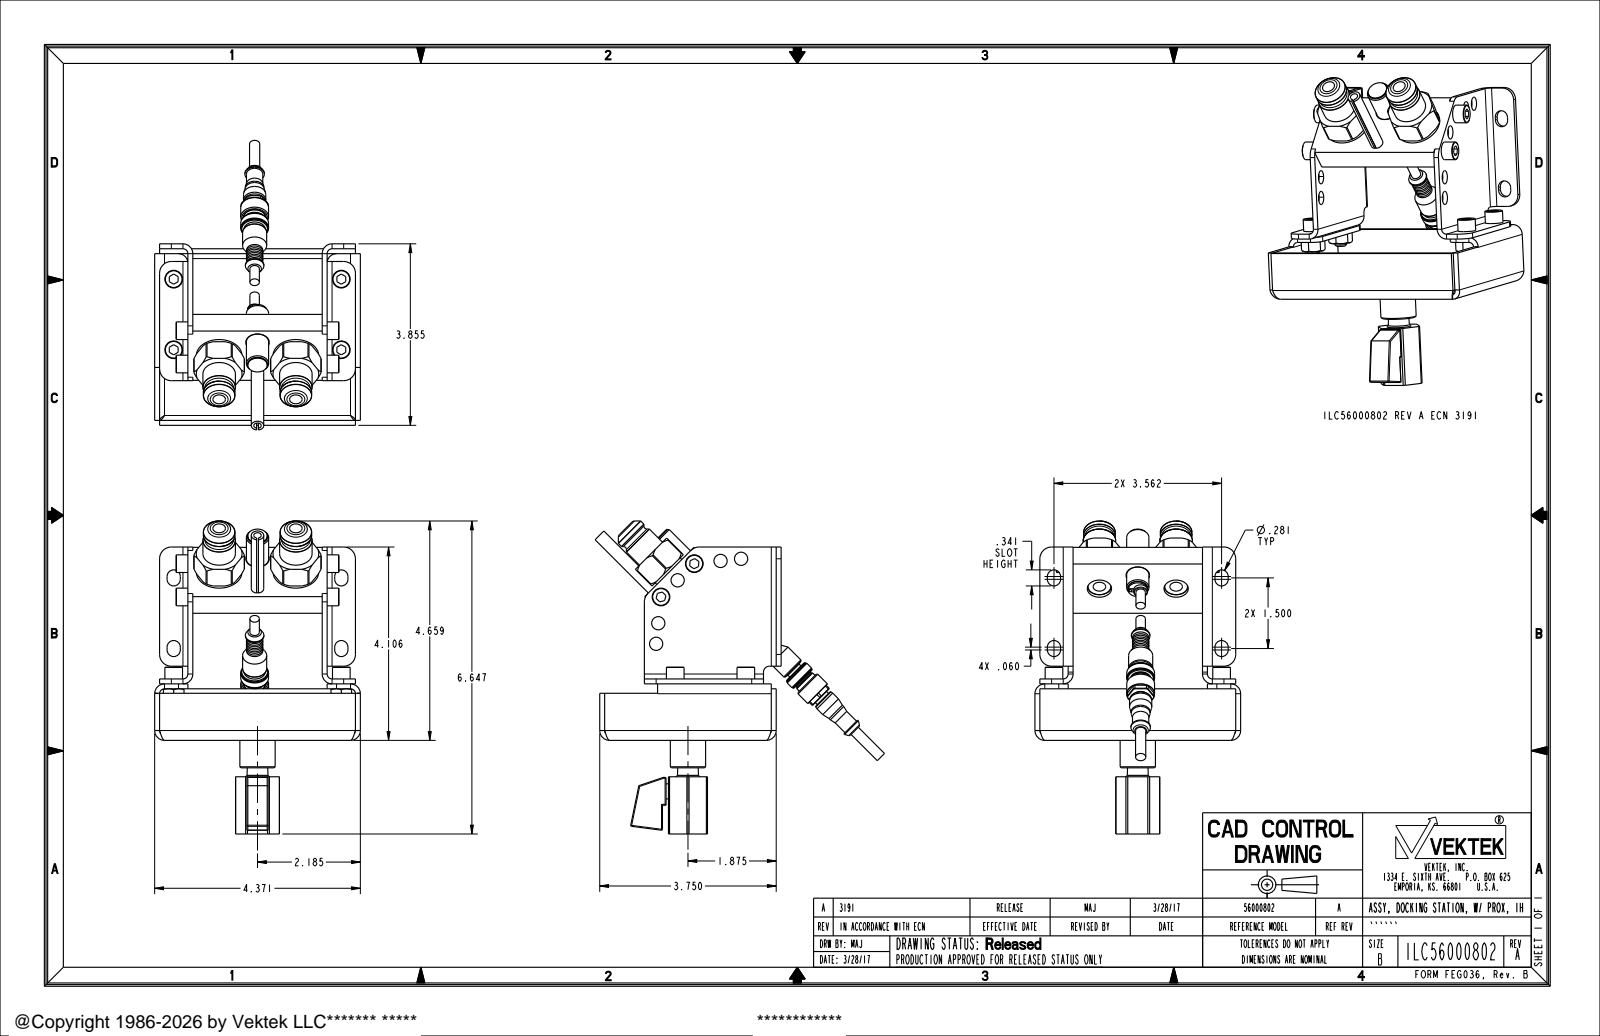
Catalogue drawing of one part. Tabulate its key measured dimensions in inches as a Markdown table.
| quantity | value |
| --- | --- |
| part name | ILC56000802 |
| STEP written by | PRO/ENGINEER BY PARAMETRIC TECHNOLOGY CORPORATION, 2013320 (AUTOMOTIVE_DESIGN) |
| units | inches |
| bodies | 4 solids, 742 faces (286 planar, 232 cylindrical, 224 other) |
| overall size | 7.558 × 6.446 × 4.371 |
| volume | 10.81 in³ |
| surface area | 156.4 in² |
| round holes (diameter × count) | 0.281 × 5, 0.266 × 2, 0.515 × 2, 0.97 × 2, 0.158 × 1, 0.25 × 1, 0.315 × 1, 0.443 × 1, 0.781 × 1 |
| round bosses / shafts (diameter × count) | 0.375 × 6, 0.25 × 4, 0.75 × 3, 0.69 × 2, 0.671 × 2, 0.413 × 2, 0.591 × 1, 0.571 × 1 |
| partial cylindrical surfaces (radius × count) | 0.02 × 18, 0.105 × 10, 0.209 × 10, 0.25 × 10, 0.141 × 8, 0.2 × 4, 0.536 × 2, 0.125 × 1 |
| main face-to-face distances | 0.105, 2.854, 0.706, 3.56, 3.645, 2.959, 0.601, 3.456, 2.75, 0.811 |
| hole center spacings | 0.439, 0.956, 1, 1.423, 2.229, 1.63, 1.871, 2.553 |
